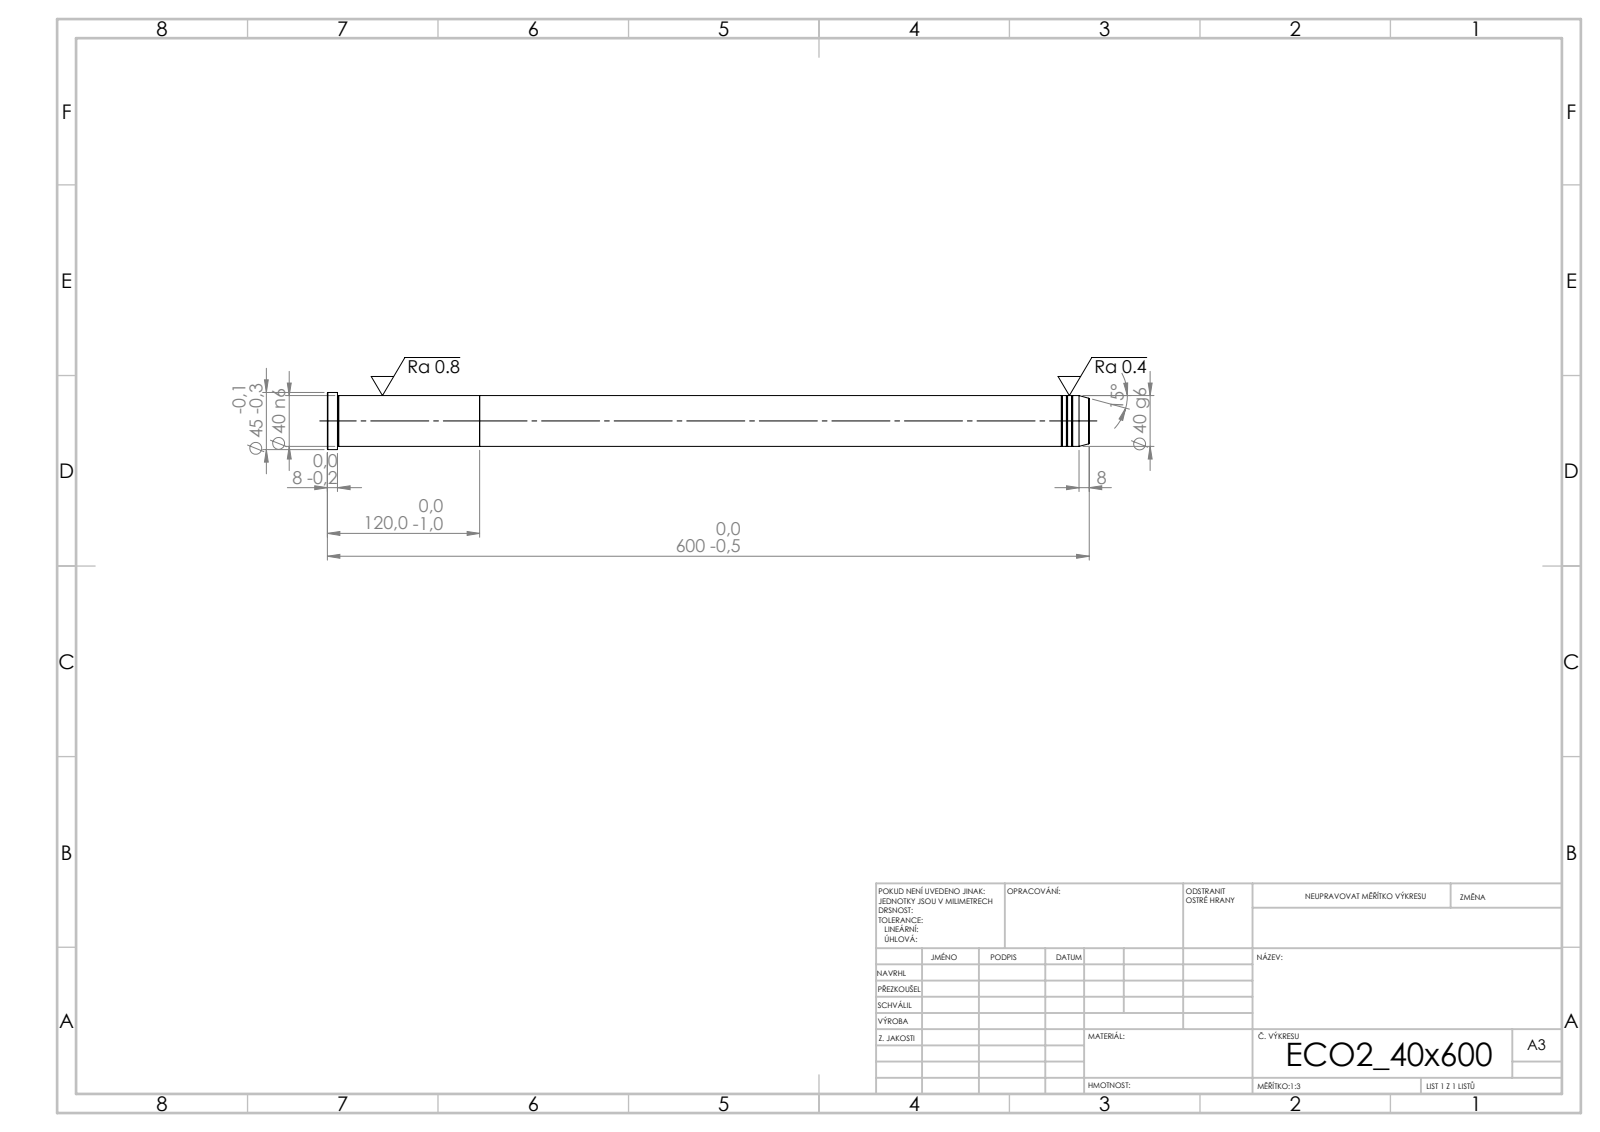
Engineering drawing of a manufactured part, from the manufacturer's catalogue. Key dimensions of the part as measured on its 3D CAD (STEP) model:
STEP written by: SolidWorks 2019 (CONFIG_CONTROL_DESIGN)
Units: millimetres
Bodies: 2 solids, 39 faces (5 planar, 12 cylindrical, 22 other)
Overall size (bounding box): 600 × 45 × 45
Volume: 755 398 mm³ · Surface area: 81 163 mm²
Round bosses / shafts (diameter × count): ⌀45 ×1, ⌀40 ×1
Main face-to-face distances: 120, 480, 600, 592, 112, 8
